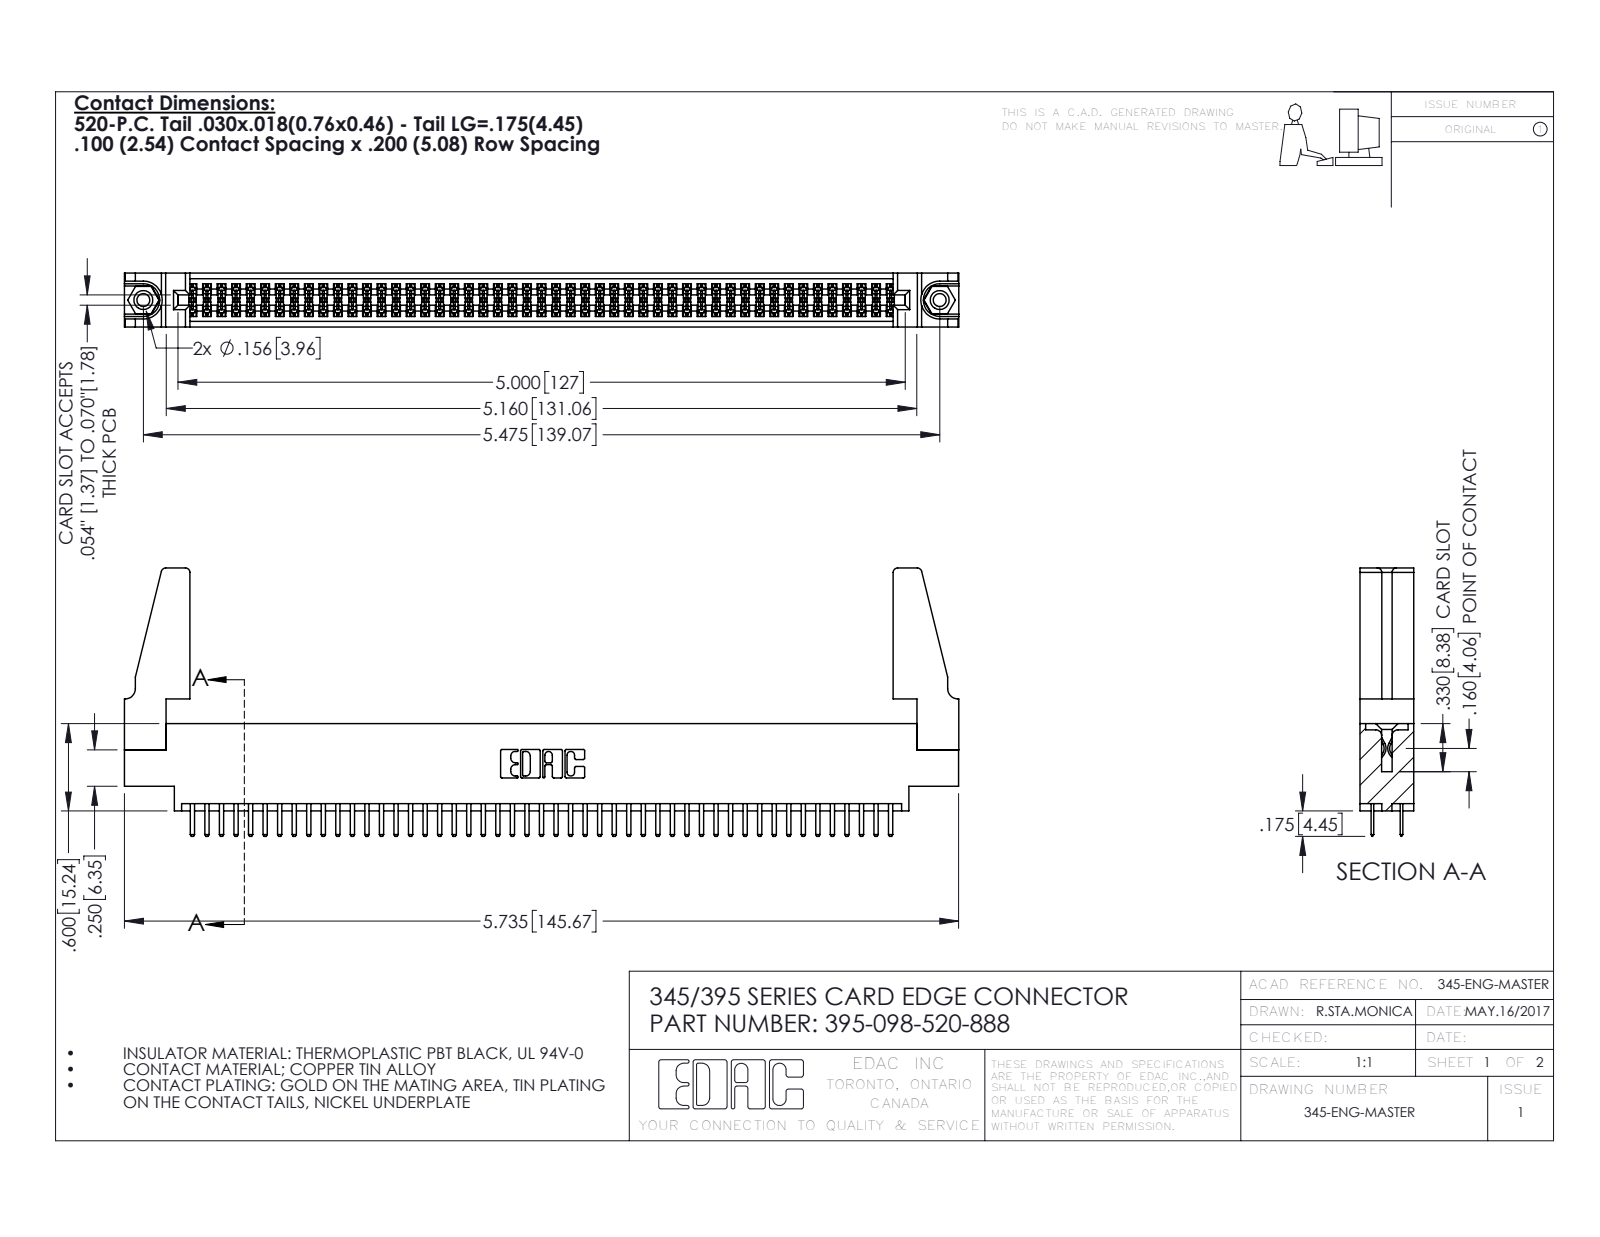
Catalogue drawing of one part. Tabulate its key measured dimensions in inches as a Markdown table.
| quantity | value |
| --- | --- |
| part name | 345-220-078_345-220-088; 395-098-520-888; 345-292-001_345-293-120; 345-250-001_345-250-001-102 (+1 more) |
| STEP written by | SolidWorks 2016 (CONFIG_CONTROL_DESIGN) |
| units | inches |
| bodies | 103 solids, 5546 faces (3586 planar, 1944 cylindrical, 16 other) |
| overall size | 5.736 × 1.845 × 0.37 |
| volume | 1.057 in³ |
| surface area | 37.35 in² |
| round holes (diameter × count) | 0.089 × 2, 0.125 × 2, 0.156 × 2, 0.064 × 1 |
| round bosses / shafts (diameter × count) | 0.155 × 2 |
| partial cylindrical surfaces (radius × count) | 0.006 × 147, 0.01 × 102, 0.01 × 22, 0.03 × 8, 0.007 × 6, 0.031 × 6, 0.026 × 3, 0.014 × 2 |
| main face-to-face distances | 0.072, 0.298, 0.37, 0.2, 0.098, 0.272, 0.025, 0.225, 0.022, 0.072 |
| hole center spacings | 0.27, 5.239, 5.475 |
